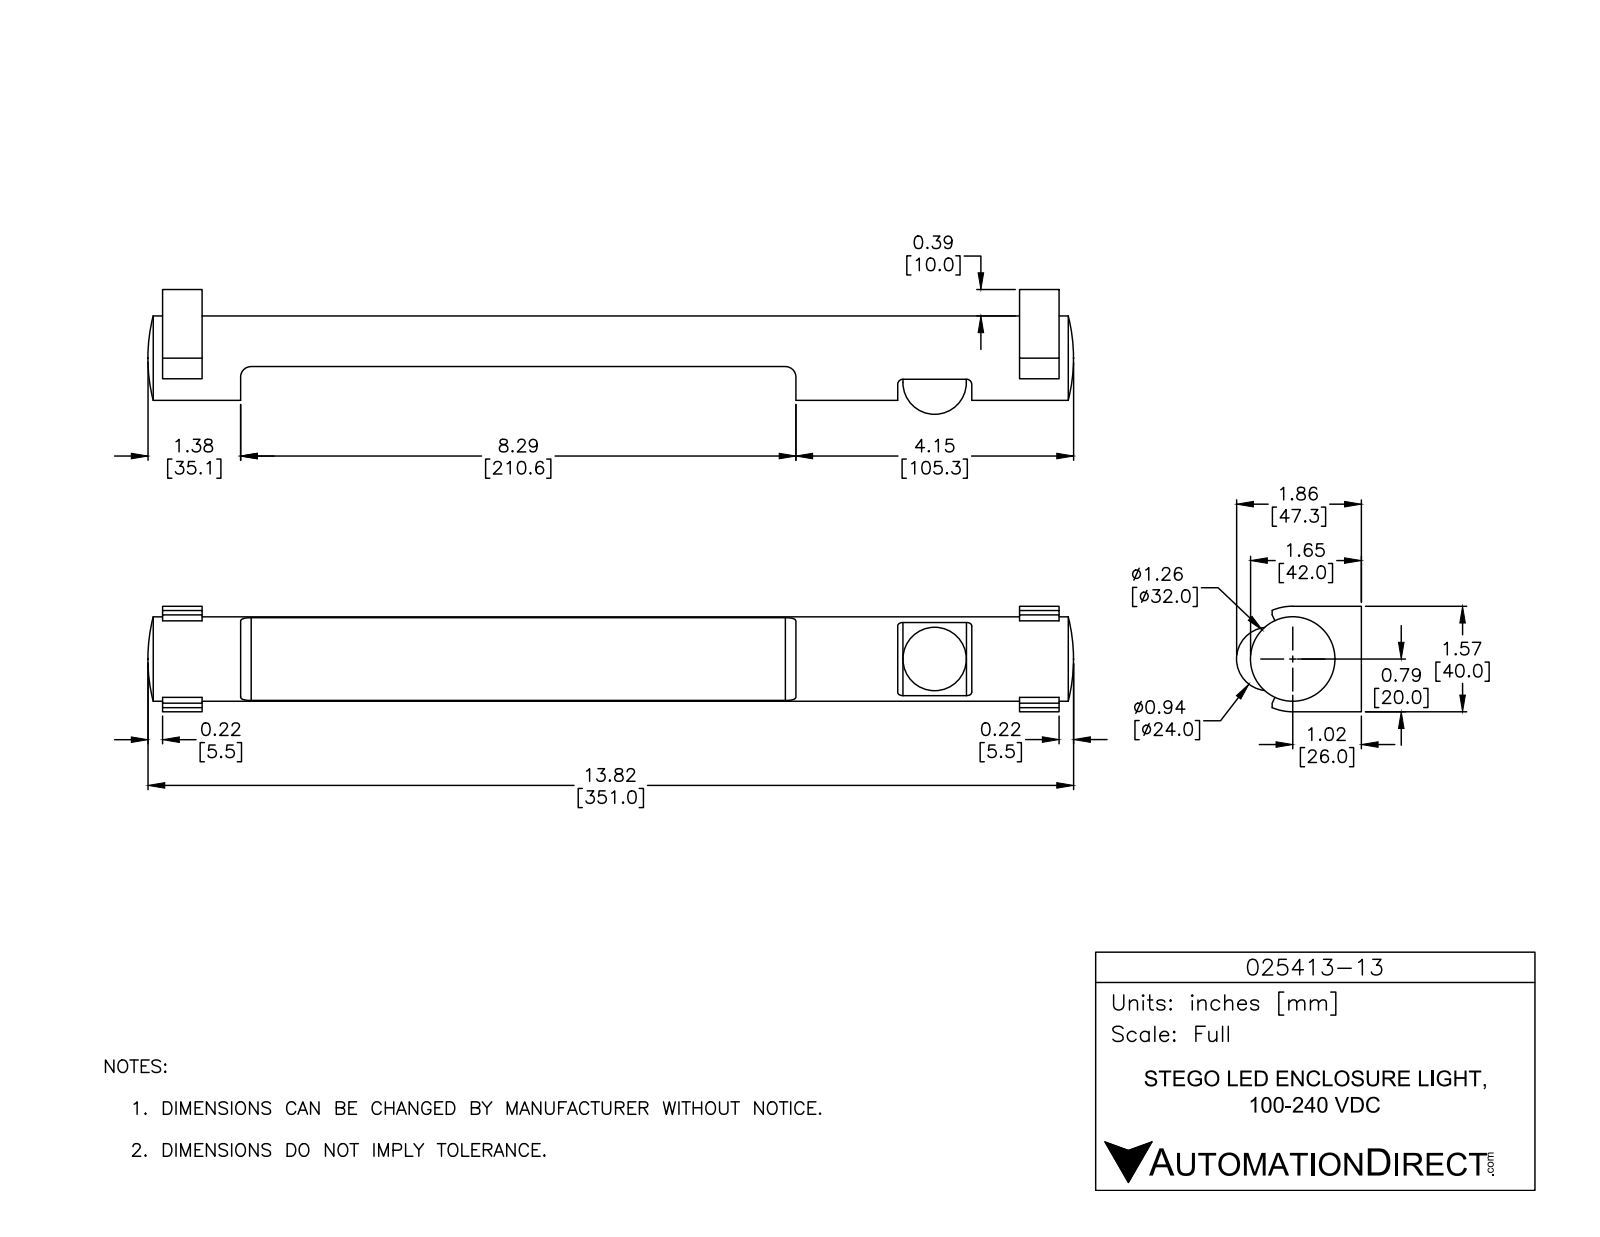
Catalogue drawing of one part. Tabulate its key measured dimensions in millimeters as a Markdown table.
| quantity | value |
| --- | --- |
| part name | PRODUCT_NAME_1 |
| STEP written by | ACIS (CONFIG_CONTROL_DESIGN) |
| units | millimeters |
| bodies | 1 solid, 74 faces (42 planar, 26 cylindrical, 6 other) |
| overall size | 351 × 47.3 × 40 |
| volume | 234 107 mm³ |
| surface area | 41 636 mm² |
| round bosses / shafts (diameter × count) | 32 × 1 |
| partial cylindrical surfaces (radius × count) | 3.1 × 4, 2 × 2, 3.75 × 2, 4 × 2, 20 × 1 |
| main face-to-face distances | 325, 15, 29.2, 40, 340, 310, 2.5, 12.5, 7.5, 32.5 |
